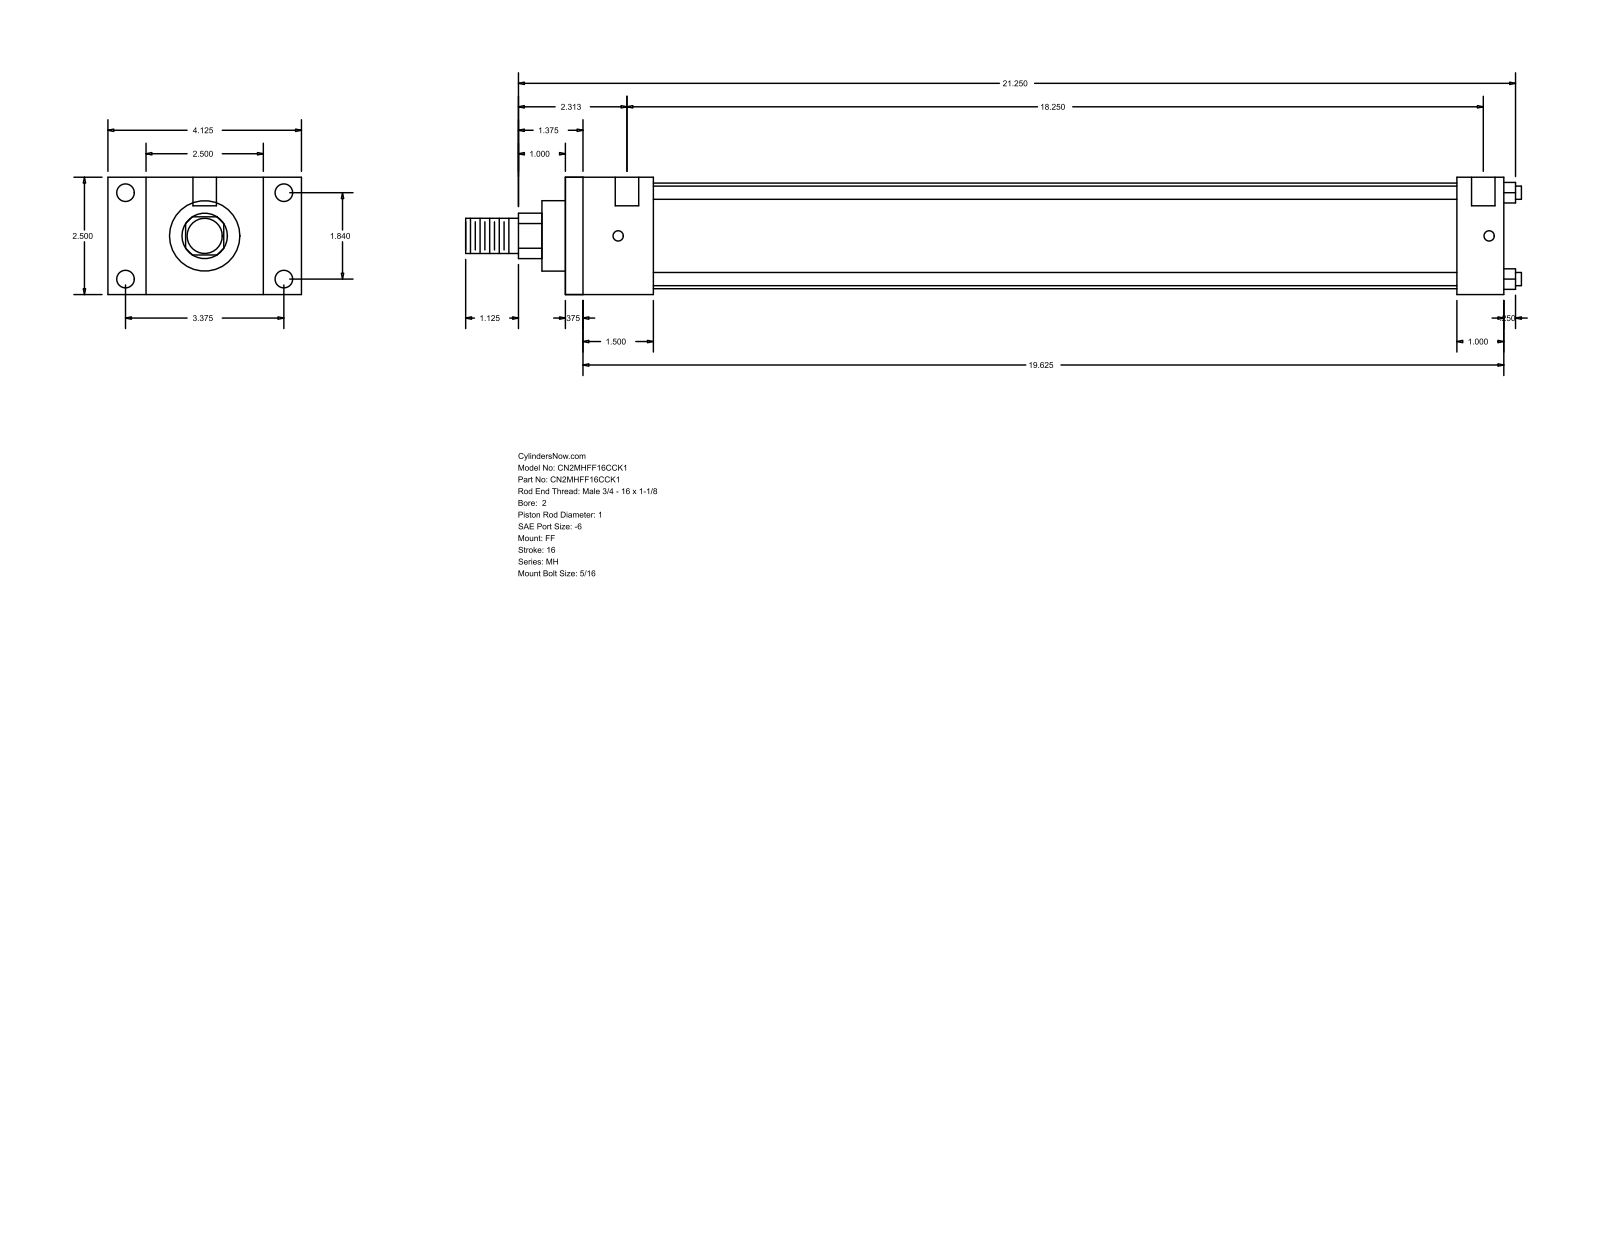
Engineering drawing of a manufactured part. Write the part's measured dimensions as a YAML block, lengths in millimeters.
part_name: "MH_FF__0200_1"
step_written_by: "GSSL Pune (CONFIG_CONTROL_DESIGN)"
units: millimeters
bodies: {solids: 0, faces: 92, planar: 64, cylindrical: 28, other: 0}
overall_size: [571.5, 104.78, 63.5]
round_holes:
  - {diameter: 5.56, count: 4}
  - {diameter: 9.53, count: 4}
  - {diameter: 12.7, count: 2}
round_bosses_or_shafts:
  - {diameter: 7.14, count: 4}
  - {diameter: 57.15, count: 1}
  - {diameter: 38.1, count: 1}
  - {diameter: 25.4, count: 1}
  - {diameter: 19.05, count: 1}
partial_cylinders:
  - {radius: 12.29, count: 1}
face_to_face_distances: [63.5, 508, 9.52, 498.48, 20.64, 25.4, 47.63, 482.6, 38.11, 473.08]
hole_center_spacings: [46.74, 85.72, 97.63, 471.48, 3.17, 4.76, 463.55, 466.72]
